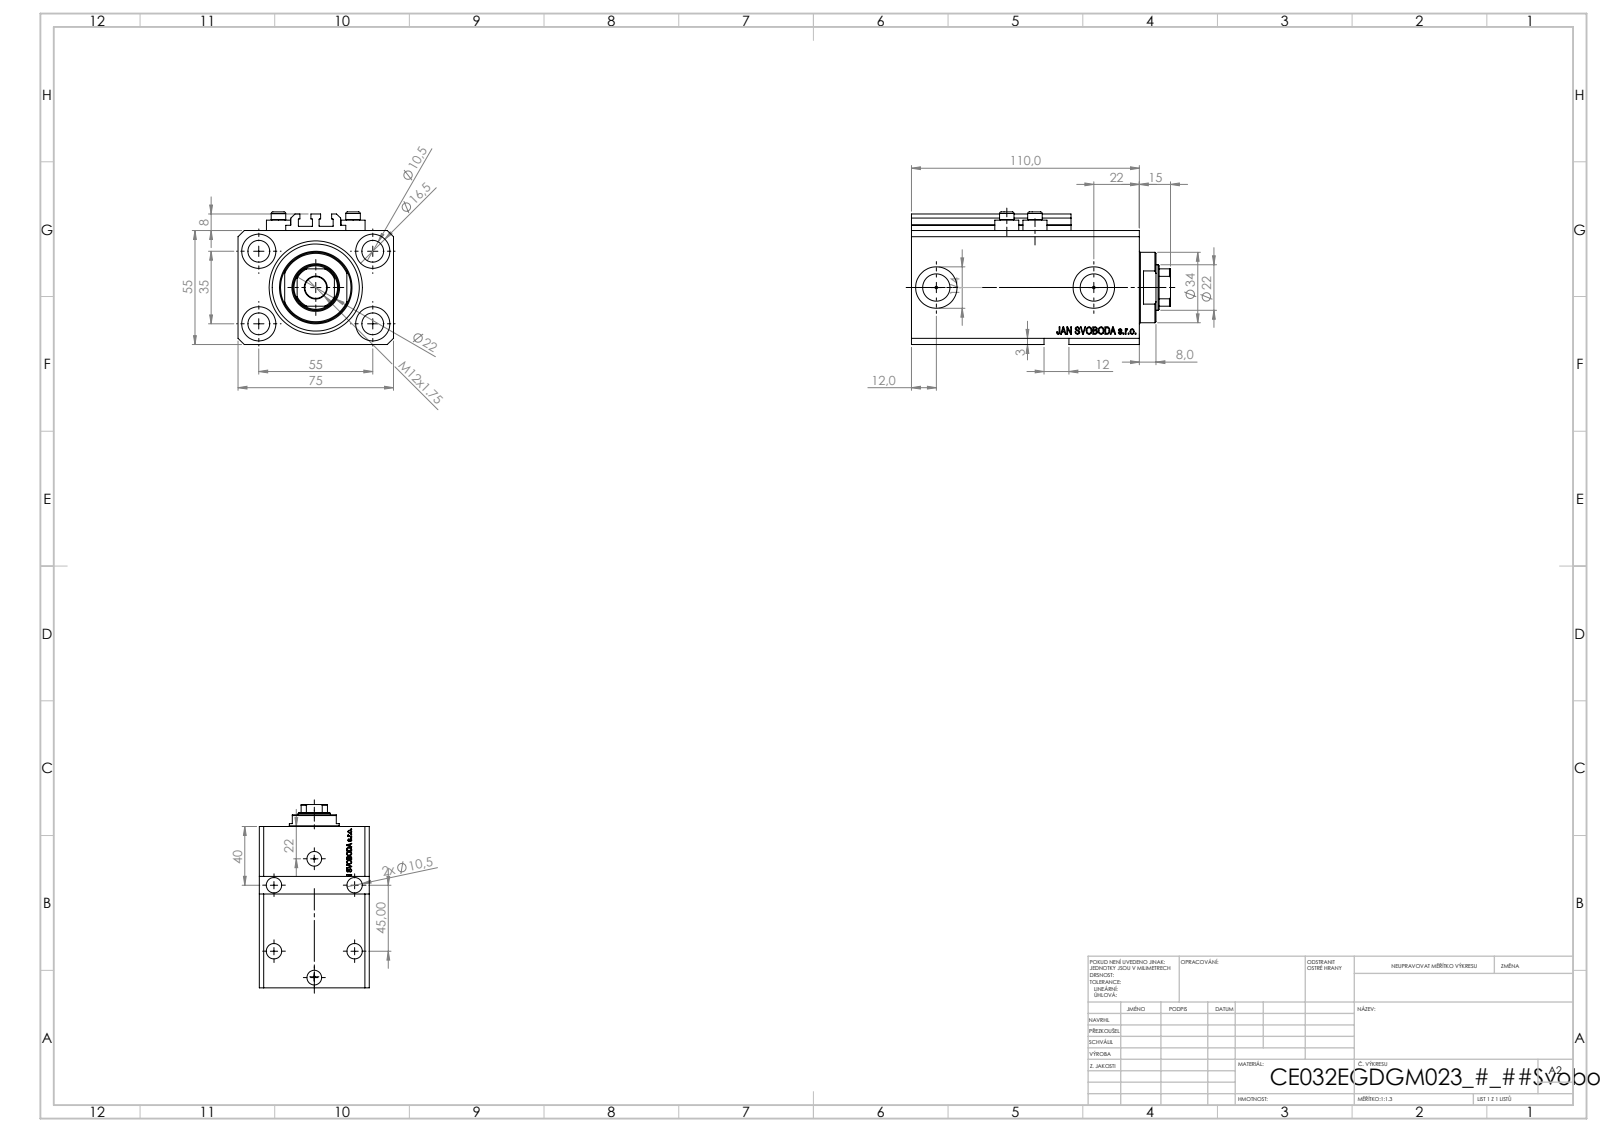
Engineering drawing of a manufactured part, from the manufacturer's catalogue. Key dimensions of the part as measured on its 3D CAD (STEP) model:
Part name (STEP PRODUCT): V250CE_C_VCP; V250CE_E_Body; ALLEN BOLT V250CE; V250CE_VC_E
STEP written by: SolidWorks 2019 (CONFIG_CONTROL_DESIGN)
Units: millimetres
Bodies: 8 solids, 1100 faces (518 planar, 158 cylindrical, 424 other)
Overall size (bounding box): 125 × 75 × 64
Volume: 377 718 mm³ · Surface area: 96 791 mm²
Round holes (diameter × count): ⌀10.5 ×9, ⌀1.25 ×4, ⌀4 ×4, ⌀16.5 ×4, ⌀10 ×2, ⌀13.16 ×2, ⌀20 ×2, ⌀22 ×1, ⌀32 ×1, ⌀45 ×1
Round bosses / shafts (diameter × count): ⌀11.6 ×4, ⌀7 ×4, ⌀34 ×1
Partial cylindrical surfaces — rounded edges, fillets, slot ends (radius × count): R0.2 ×10, R10.5 ×1
Main face-to-face distances: 55, 75, 15, 110, 95, 9.9, 3, 85.1, 100.1, 57
Hole centre spacings: 32.6, 32.87, 55, 68.74, 13.6, 14.09, 23.05, 25.81
